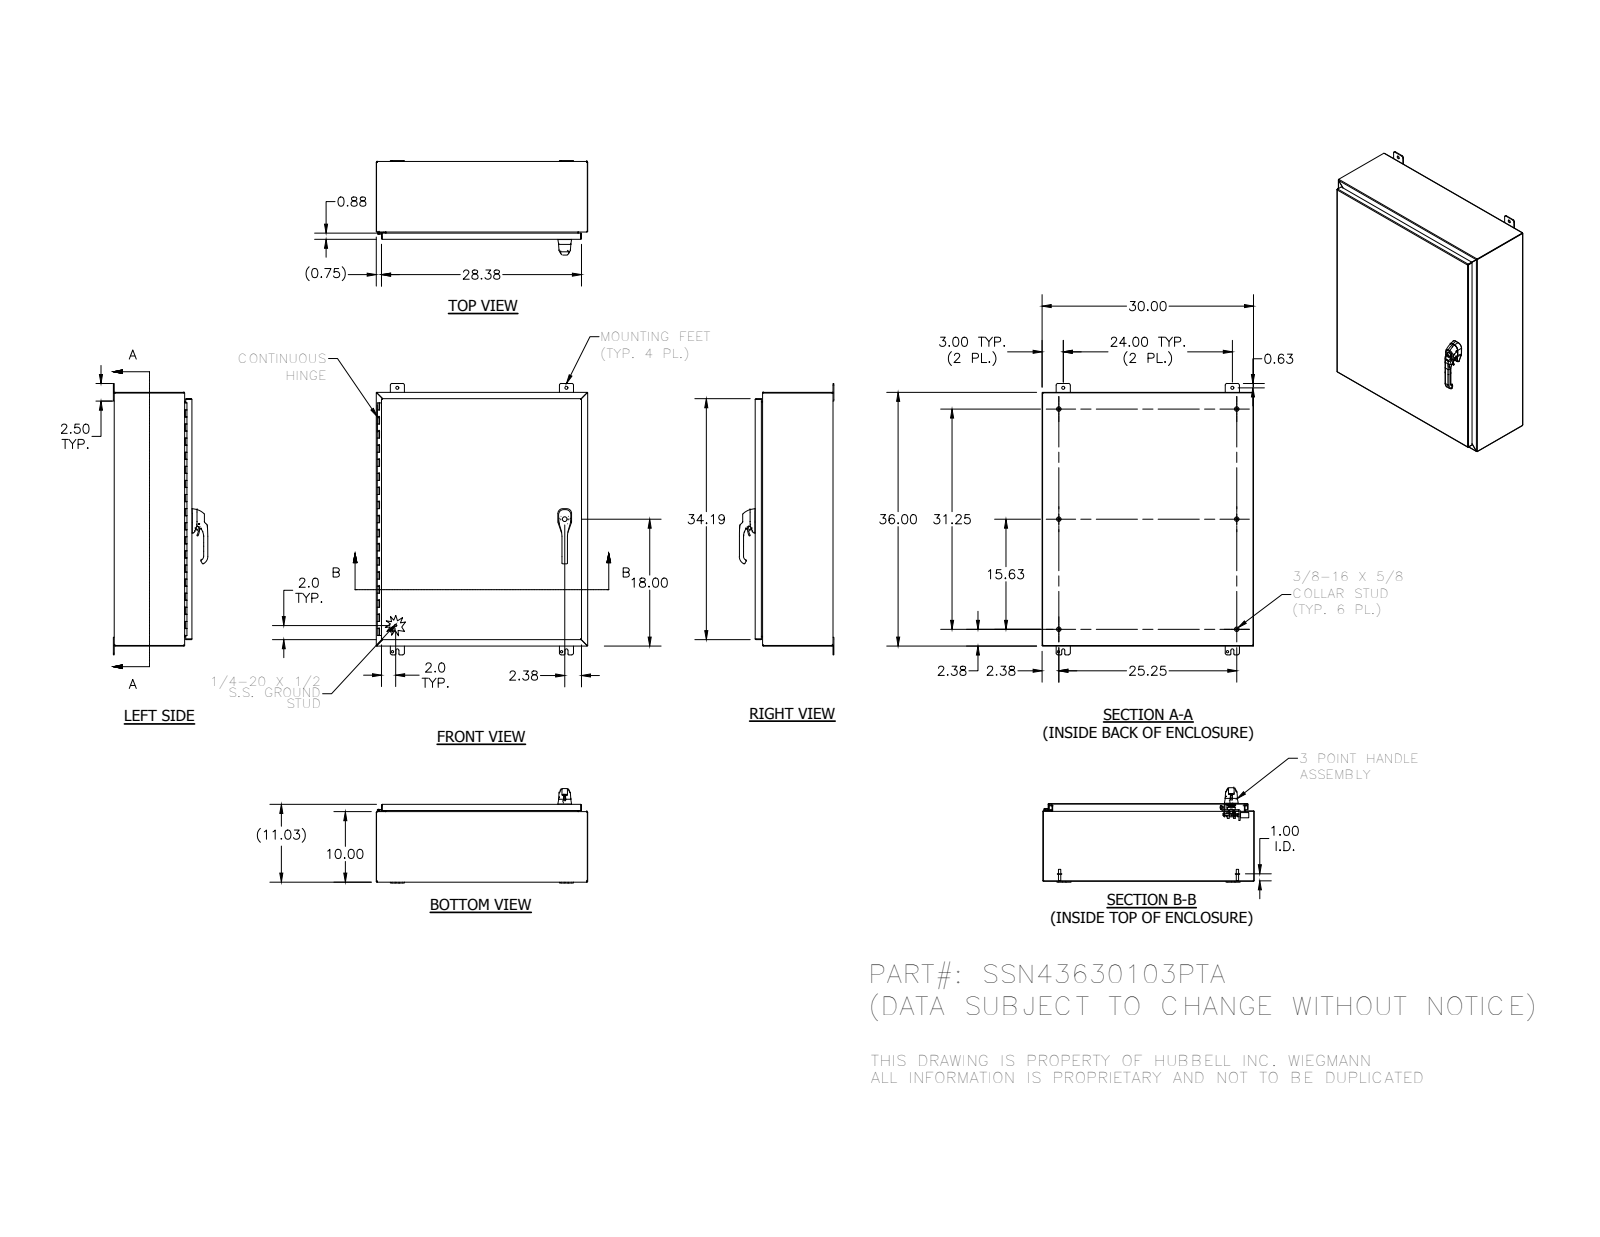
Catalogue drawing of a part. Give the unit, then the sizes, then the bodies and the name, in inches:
Units: inches
Overall size (bounding box): 38.5 × 30 × 13.408
Round holes (diameter × count): ⌀0.262 ×8, ⌀0.187 ×4, ⌀0.313 ×4, ⌀0.438 ×4, ⌀0.213 ×3, ⌀0.281 ×3, ⌀0.241 ×2, ⌀0.25 ×2, ⌀0.252 ×2, ⌀0.315 ×2, ⌀0.4 ×2, ⌀0.402 ×2
Round bosses / shafts (diameter × count): ⌀0.625 ×6, ⌀0.33 ×6, ⌀0.236 ×3, ⌀1 ×2, ⌀0.563 ×2, ⌀0.533 ×2, ⌀0.531 ×2, ⌀0.5 ×2
Partial cylindrical surfaces — rounded edges, fillets, slot ends (radius × count): R0.02 ×172, R0.012 ×113, R0.125 ×26, R0.031 ×24, R0.019 ×21, R0.105 ×20, R0.25 ×20, R0.025 ×16
Main face-to-face distances: 0.074, 10.959, 10.885, 11.033, 29.926, 35.926, 29.852, 30, 9.926, 1.033
Hole centre spacings: 0.38, 0.492, 0.76, 1.593, 24, 36, 43.267, 0.886
Volume: 312.1 in³ · Surface area: 8 155 in²
Bodies: 58 solids, 3229 faces (1088 planar, 1352 cylindrical, 789 other)
Part name (STEP PRODUCT): 1091-903_AF0_2; SSN436303PTALID; 34839; HFW32451 (+8 more)
STEP written by: SolidWorks 2014 (AUTOMOTIVE_DESIGN)
